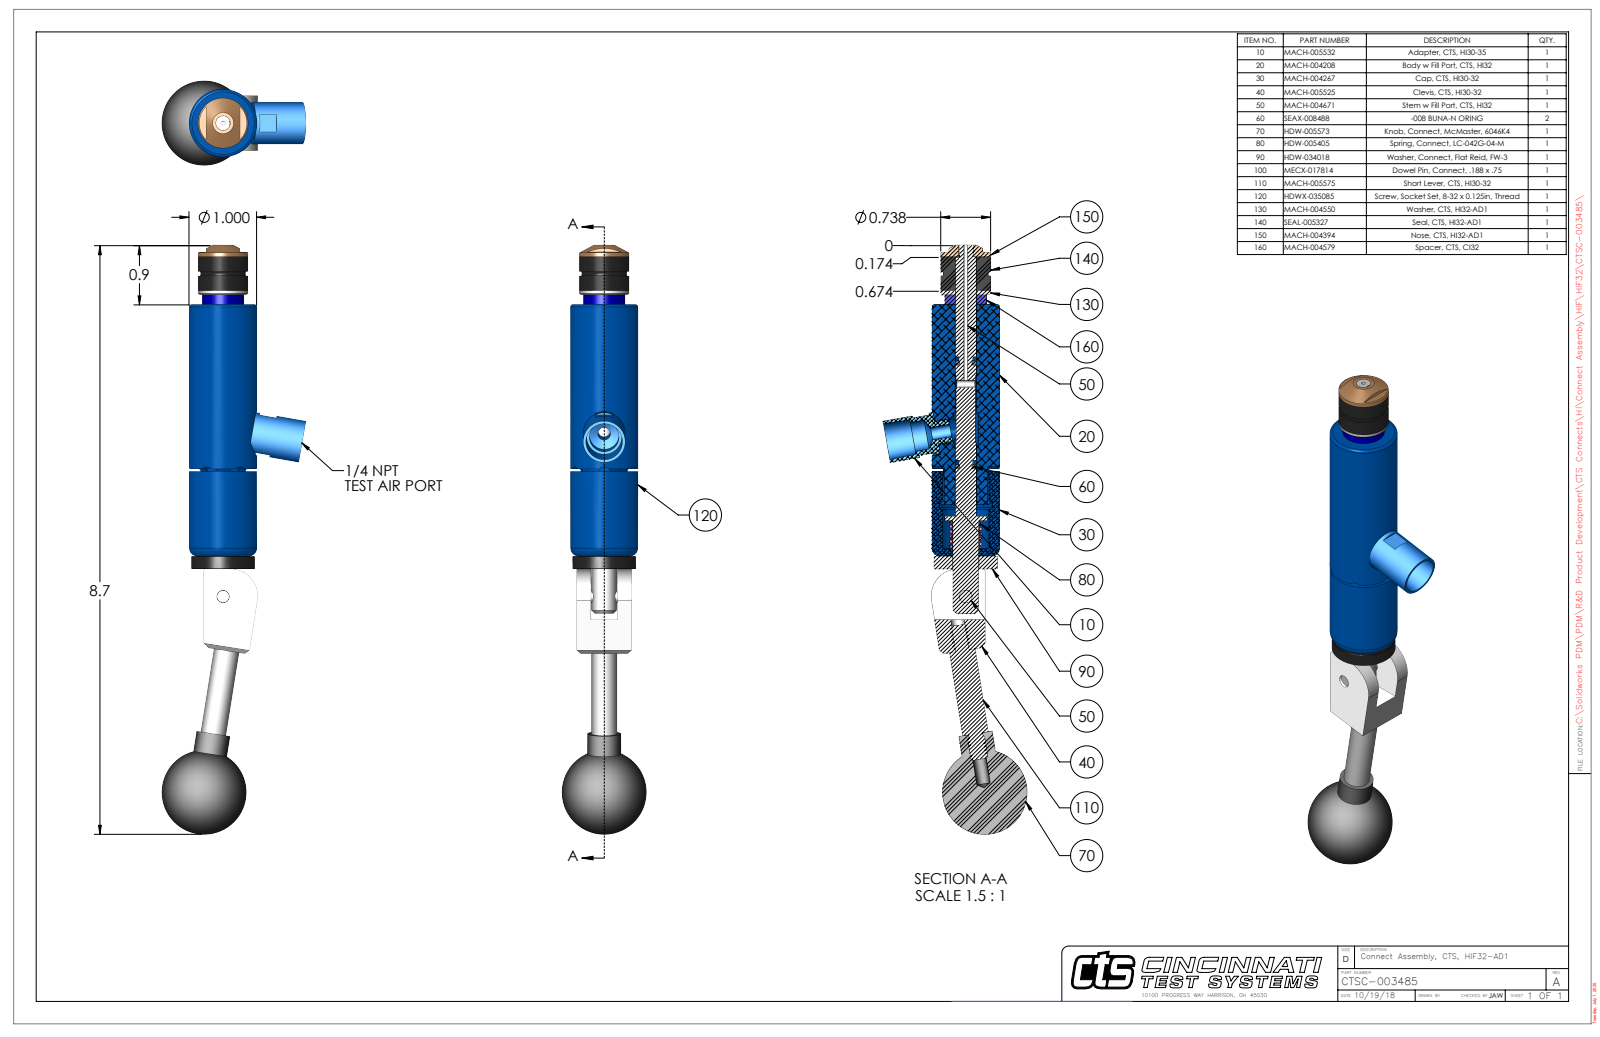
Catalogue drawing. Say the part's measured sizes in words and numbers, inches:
The part is named "CTSC-003485". Its 3-D file was written by "SolidWorks 2023 (AUTOMOTIVE_DESIGN)". It is 10 solids with 298 faces: 111 planar, 123 cylindrical and 64 other. Overall it measures 8.704 by 2.128 by 1.25 inches. Its volume is 5.186 cubic inches and its surface area 41.81 square inches. Round holes: 2 of diameter 0.201, 1 of diameter 0.063, 1 of diameter 0.109, 1 of diameter 0.136, 1 of diameter 0.15, 1 of diameter 0.187, 1 of diameter 0.189, 1 of diameter 0.213, 1 of diameter 0.31, 1 of diameter 0.314, 1 of diameter 0.316, 1 of diameter 0.385. Round bosses or shafts: 2 of diameter 0.25, 2 of diameter 0.201, 1 of diameter 1, 1 of diameter 0.936, 1 of diameter 0.738, 1 of diameter 0.62, 1 of diameter 0.618, 1 of diameter 0.5. Partial cylindrical surfaces (rounded edges, fillets, slot ends): 6 of radius 0.093, 2 of radius 0.029, 1 of radius 0.063, 1 of radius 0.325, 1 of radius 0.4, 1 of radius 0.457. The main face-to-face distances are 0.21, 0.602, 3.719, 0.812, 0.702, 4.42, 0.5, 4.608, 3.906, 0.187. The hole center spacings are 0.599, 1.658, 2.252.
